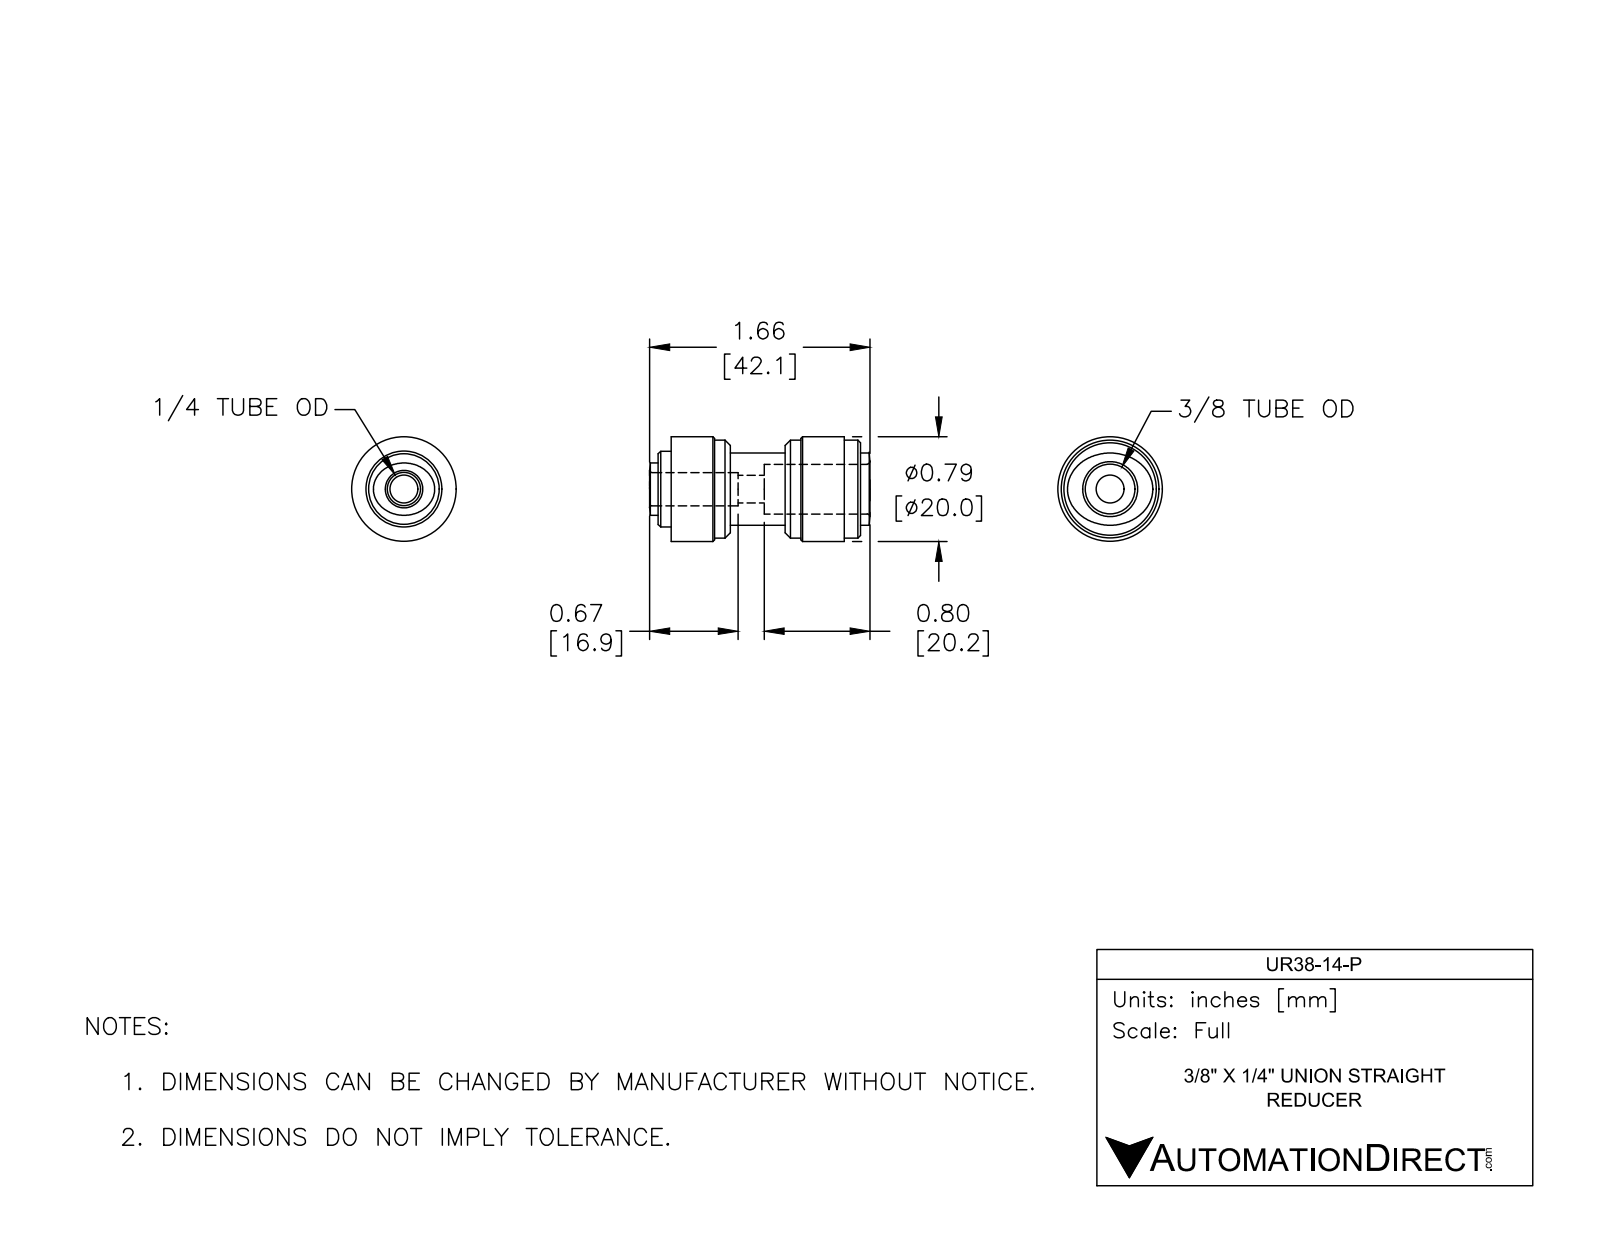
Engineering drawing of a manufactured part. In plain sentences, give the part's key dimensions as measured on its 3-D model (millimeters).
The part is named "UR38-14-P". Its 3-D file was written by "SolidWorks 2017 (AUTOMOTIVE_DESIGN)". It is 1 solid with 54 faces: 10 planar, 20 cylindrical and 24 other. Overall it measures 42.1 by 20 by 20 millimeters. Its volume is 8 000 cubic millimeters and its surface area 4 079 square millimeters. Round holes: 1 of diameter 5.3, 1 of diameter 6.4, 1 of diameter 9.5. Round bosses or shafts: 1 of diameter 20, 1 of diameter 18.7, 1 of diameter 14.5, 1 of diameter 13.8. The main face-to-face distances are 21.8, 11.3, 10.5, 14.4, 24.9, 36.2, 20.3, 38.7, 24.3, 13.8.
